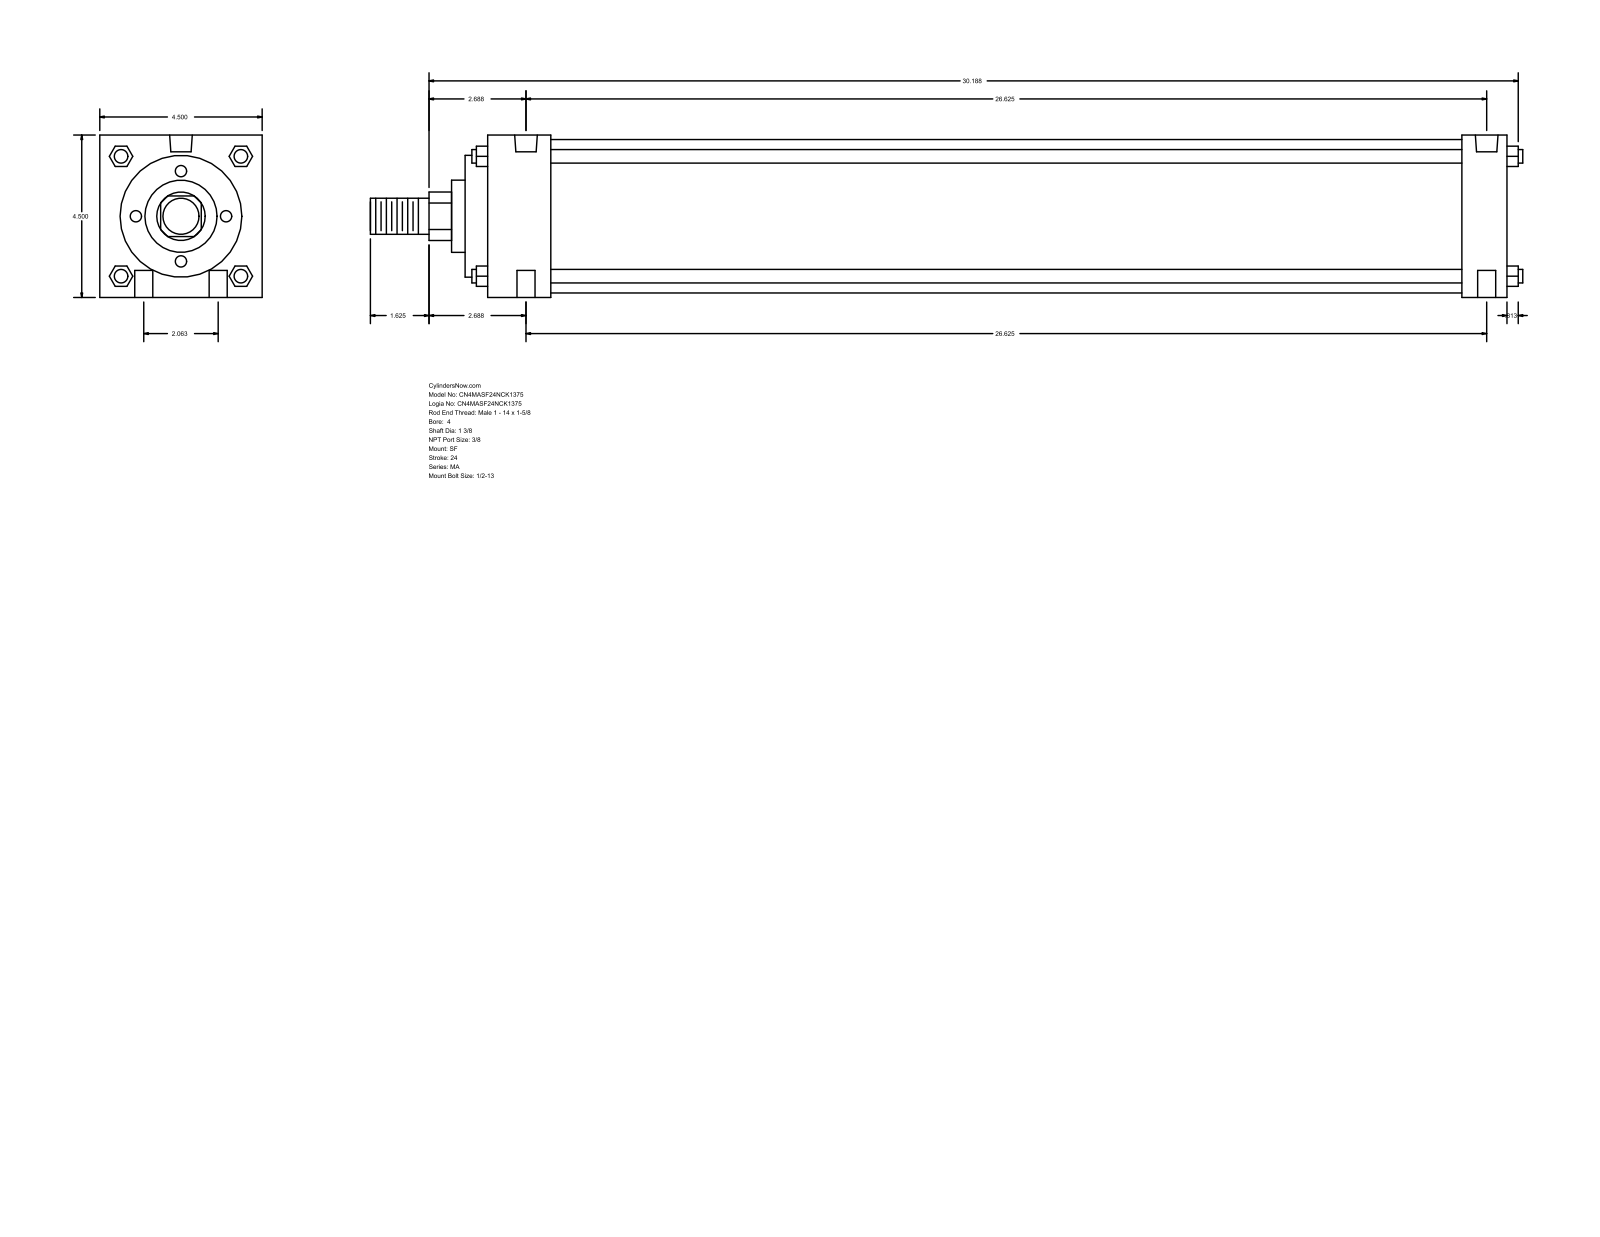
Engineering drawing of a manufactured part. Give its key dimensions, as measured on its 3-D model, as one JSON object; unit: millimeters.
{"part_name": "MA_SF__0400_1.375", "step_written_by": "GSSL Pune (CONFIG_CONTROL_DESIGN)", "units": "millimeters", "bodies": {"solids": 0, "faces": 126, "planar": 95, "cylindrical": 31, "other": 0}, "overall_size": [811.21, 114.3, 114.3], "round_holes": [[12.7, 4], [11.11, 2], [15.93, 2]], "round_bosses_or_shafts": [[9.53, 4], [107.95, 1], [85.72, 1], [50.8, 1], [34.92, 1], [25.4, 1]], "partial_cylinders_radius": [[17.06, 1]], "face_to_face_distances": [114.3, 717.56, 15.87, 733.43, 701.68, 685.81, 31.75, 60.32, 44.45, 641.36], "hole_center_spacings": [26.19, 676.79, 676.28, 52.38, 678.31, 666.74]}
